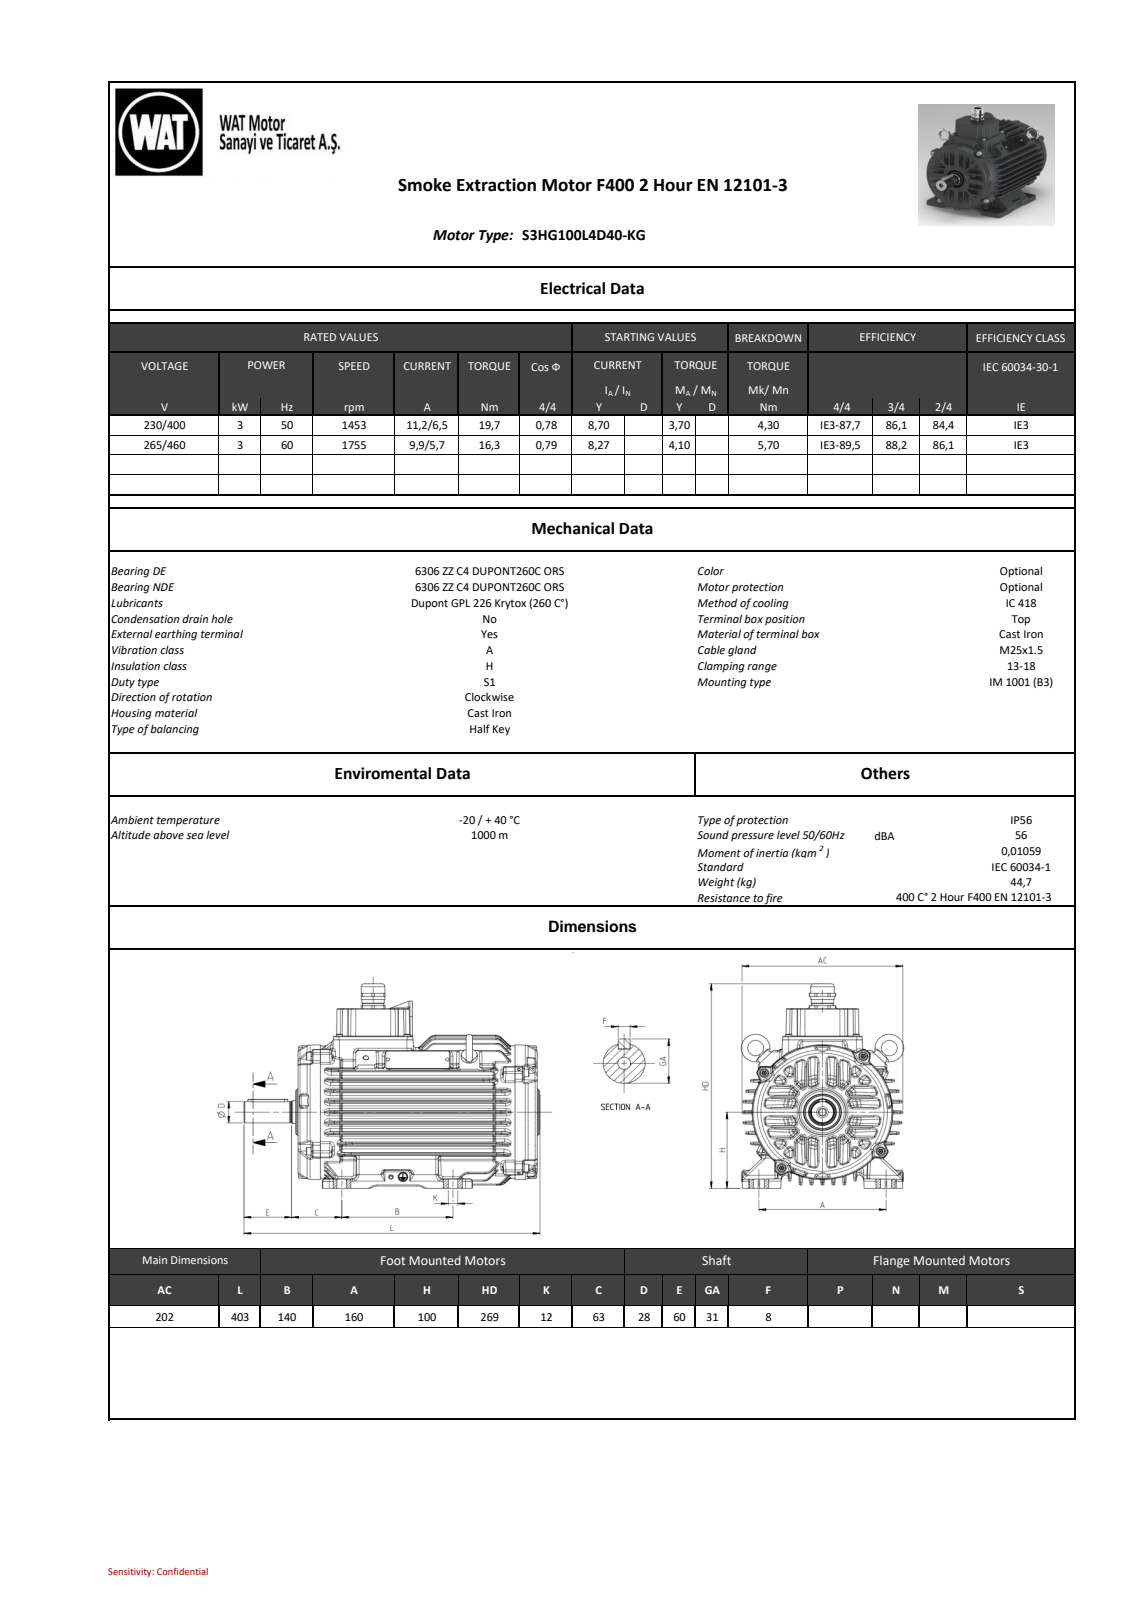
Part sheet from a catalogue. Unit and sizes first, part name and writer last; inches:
Units: inches
Overall size (bounding box): 15.846 × 10.579 × 8.043
Round holes (diameter × count): ⌀0.197 ×8, ⌀0.13 ×4, ⌀0.098 ×2, ⌀0.268 ×2, ⌀0.165 ×1, ⌀0.413 ×1, ⌀0.709 ×1, ⌀1.299 ×1, ⌀1.693 ×1
Round bosses / shafts (diameter × count): ⌀0.465 ×8, ⌀0.394 ×4, ⌀0.385 ×4, ⌀0.315 ×4, ⌀0.787 ×2, ⌀6.85 ×1, ⌀1.85 ×1, ⌀1.181 ×1
Partial cylindrical surfaces — rounded edges, fillets, slot ends (radius × count): R0.118 ×403, R0.059 ×110, R0.079 ×86, R0.071 ×48, R0.039 ×38, R0.01 ×27, R0.197 ×20, R0.02 ×12
Main face-to-face distances: 0.532, 0.536, 1.068, 3.099, 2.031, 2.563, 1.607, 1.075, 0.539, 1.492
Hole centre spacings: 3.524, 4.983, 1.223, 4.043, 5.772, 6.94, 7.047, 1.083
Bodies: 0 solids, 5062 faces (686 planar, 1159 cylindrical, 3217 other)
Part name (STEP PRODUCT): 26032C0836B7xhy9
STEP written by: SIEMENS PLM Software NX 11.0 (AUTOMOTIVE_DESIGN)
